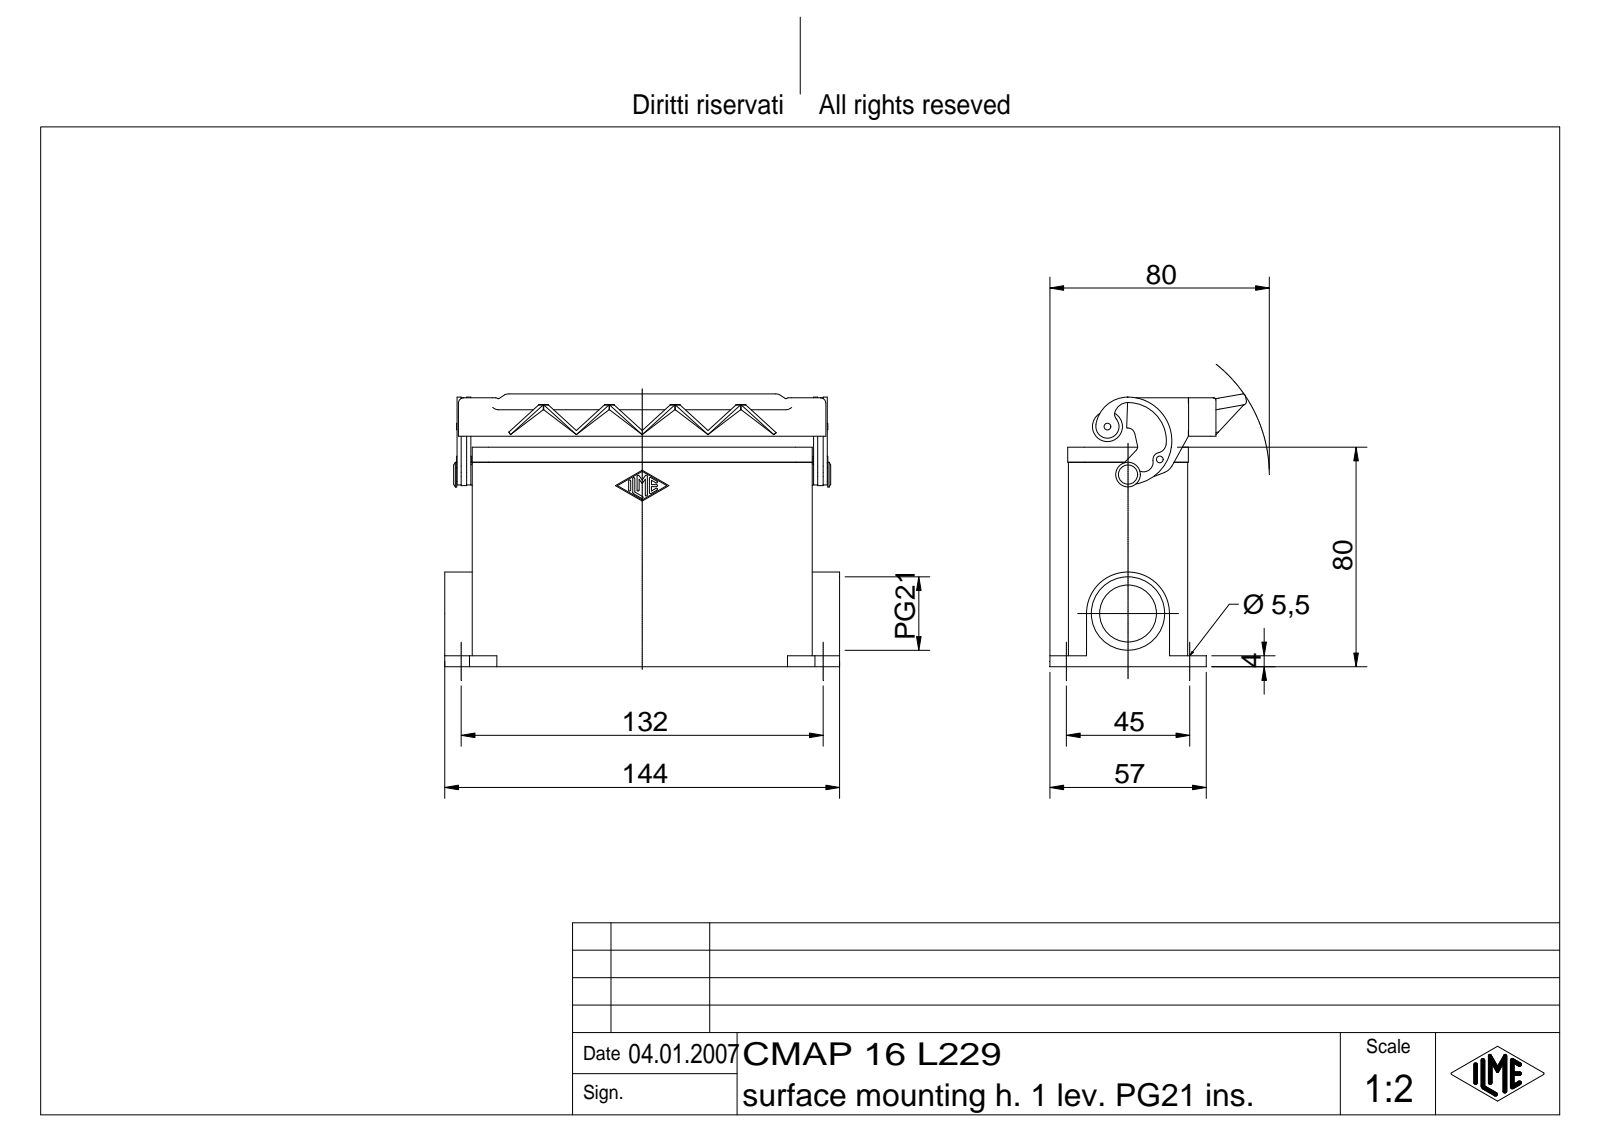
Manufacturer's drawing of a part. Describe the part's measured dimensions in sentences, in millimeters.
The part is named "CMAP 16 L229". Its 3-D file was written by "Autodesk Inventor 7 (AUTOMOTIVE_DESIGN)". It is 4 solids with 468 faces: 194 planar, 125 cylindrical and 149 other. Overall it measures 144 by 99.42 by 71.7 millimeters. Its volume is 148 454 cubic millimeters and its surface area 82 832 square millimeters. Round holes: 4 of diameter 5.5, 1 of diameter 2, 1 of diameter 29.48, 1 of diameter 35.48. Round bosses or shafts: 1 of diameter 11, 1 of diameter 9, 1 of diameter 5, 1 of diameter 3, 1 of diameter 2.5. Partial cylindrical surfaces (rounded edges, fillets, slot ends): 14 of radius 0.38, 12 of radius 2, 8 of radius 6, 7 of radius 1, 5 of radius 1.5, 4 of radius 3, 3 of radius 2.5, 2 of radius 3.5. The main face-to-face distances are 3, 40.5, 43.5, 4, 37.5, 3.25, 10.5, 74.5, 70.5, 121. The hole center spacings are 45, 132, 139.46, 53.04.
